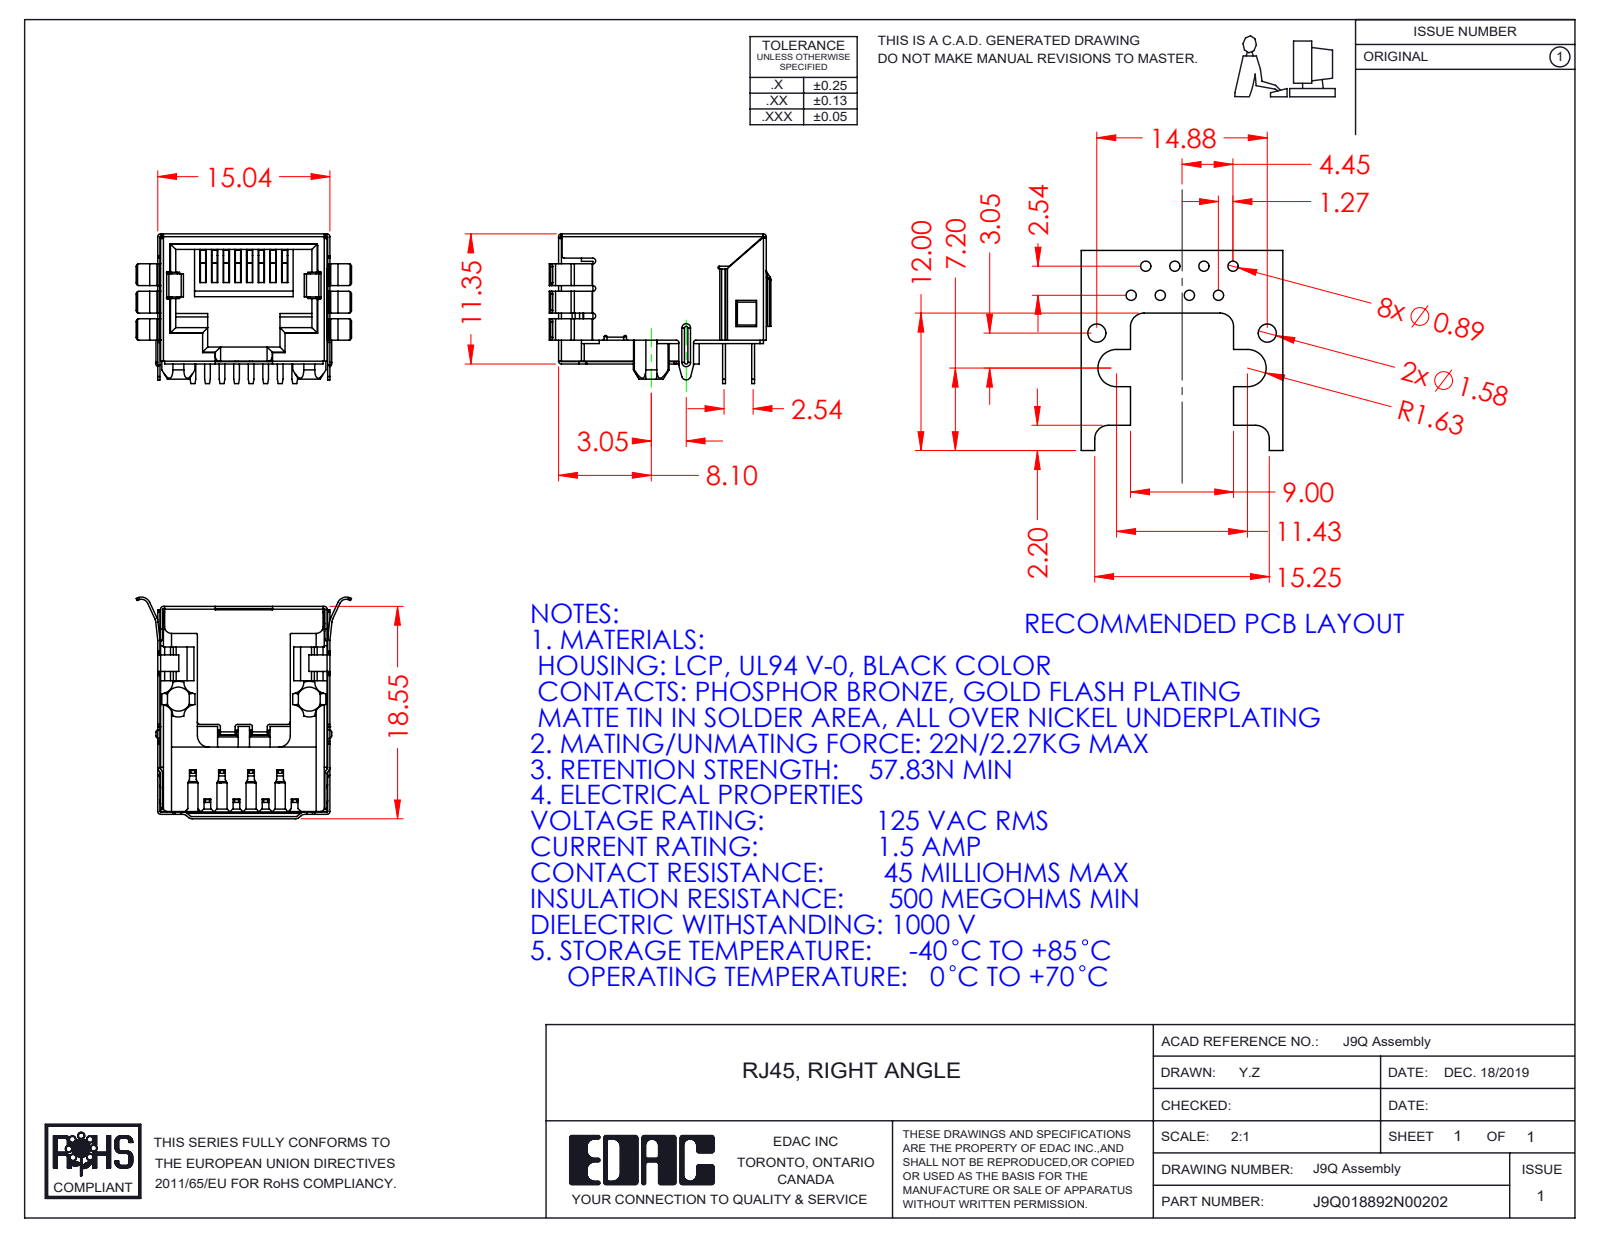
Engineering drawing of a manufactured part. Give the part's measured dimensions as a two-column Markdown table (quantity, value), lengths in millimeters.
| quantity | value |
| --- | --- |
| part name | 9Q Contact Lock; J9Q018892N00202; 9Q Contacts; 9Q Shield (+1 more) |
| STEP written by | SolidWorks 2016 (CONFIG_CONTROL_DESIGN) |
| units | millimeters |
| bodies | 11 solids, 1339 faces (949 planar, 369 cylindrical, 21 other) |
| overall size | 19.36 × 18.81 × 13.07 |
| volume | 1 193 mm³ |
| surface area | 4 818 mm² |
| partial cylindrical surfaces (radius × count) | 0.1 × 43, 0.2 × 35, 0.25 × 34, 0.15 × 24, 0.5 × 19, 0.3 × 14, 0.6 × 8, 1.05 × 8 |
| main face-to-face distances | 14.59, 14.54, 14.84, 14.34, 14.79, 0.5, 11.15, 14.29, 14.64, 15.04 |
